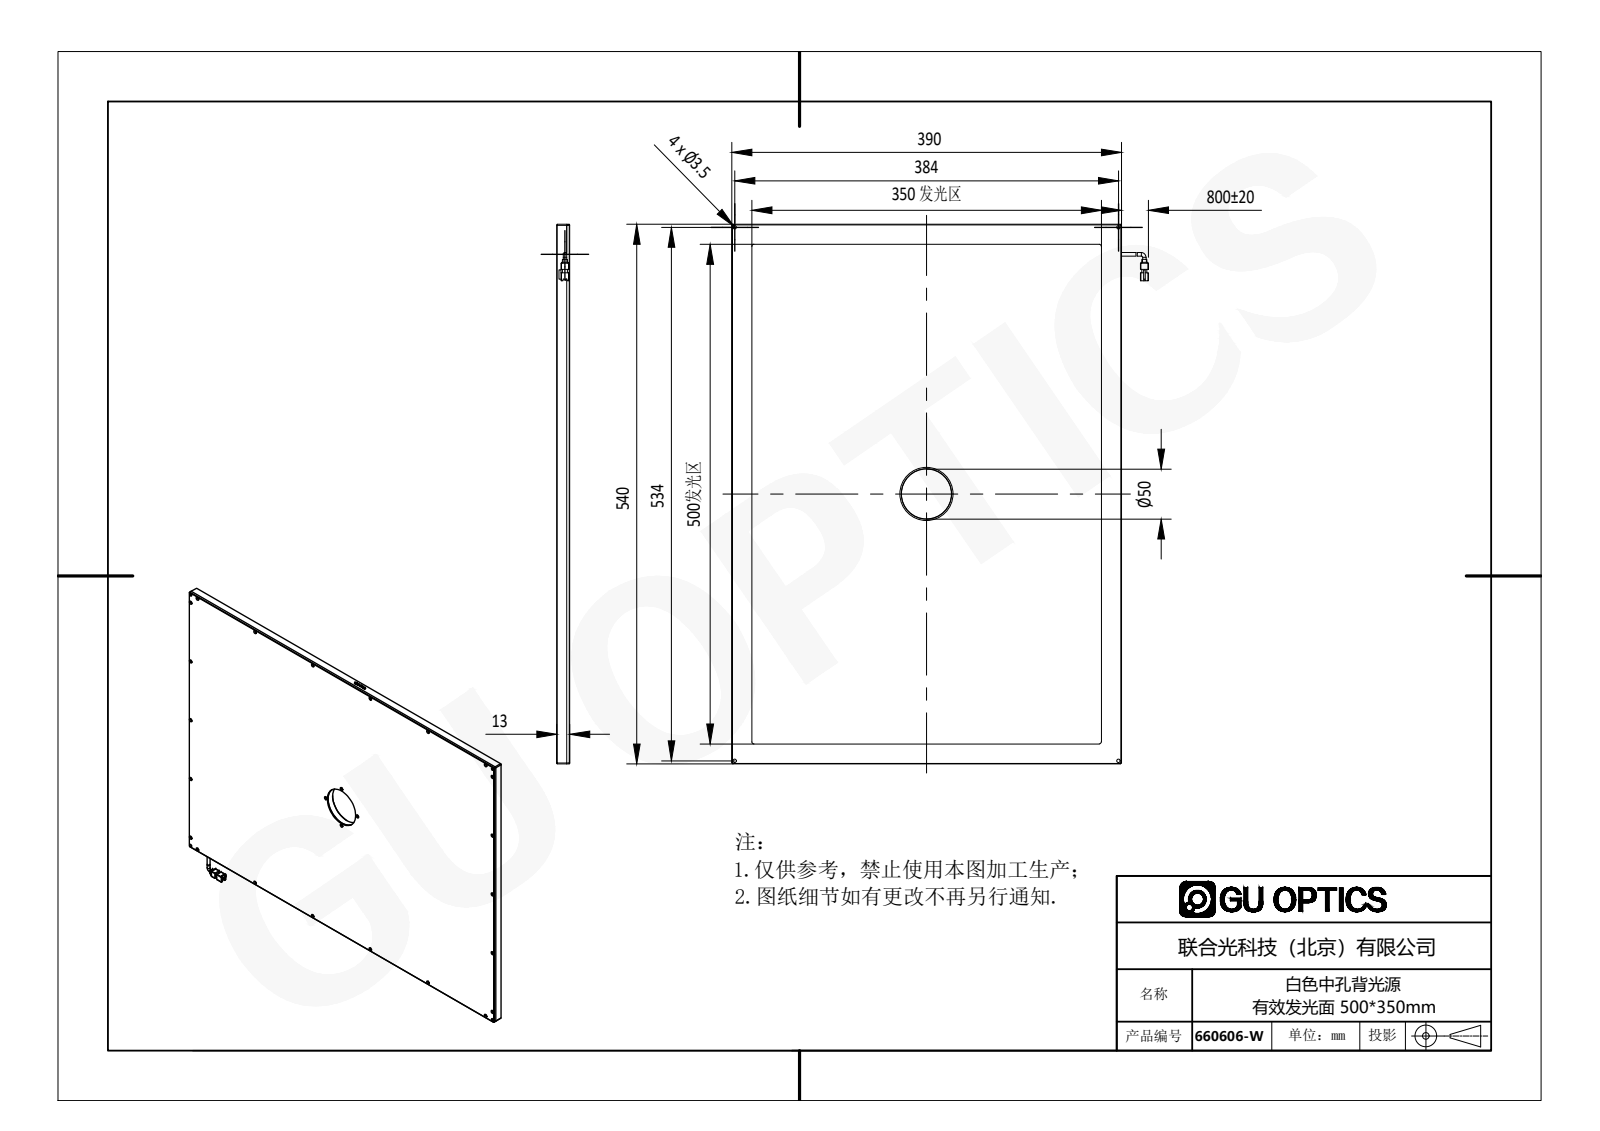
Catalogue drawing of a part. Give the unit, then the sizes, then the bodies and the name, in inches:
Units: inches
Overall size (bounding box): 21.26 × 16.417 × 0.512
Round holes (diameter × count): ⌀0.079 ×26, ⌀0.063 ×22, ⌀0.094 ×22, ⌀0.138 ×4, ⌀1.969 ×1, ⌀2.087 ×1, ⌀2.37 ×1
Round bosses / shafts (diameter × count): ⌀0.138 ×2, ⌀2.362 ×1
Partial cylindrical surfaces — rounded edges, fillets, slot ends (radius × count): R0.02 ×8, R0.039 ×6, R0.059 ×4, R0.079 ×4
Main face-to-face distances: 0.256, 0.118, 0.374, 0.512, 0.138, 0.394, 0.079, 0.236, 0.315, 15.118
Hole centre spacings: 4.016, 15.643, 0.472, 3.543, 8.031, 15.118, 17.119, 21.32
Volume: 127.2 in³ · Surface area: 1 462 in²
Bodies: 7 solids, 987 faces (622 planar, 204 cylindrical, 161 other)
Part name (STEP PRODUCT): 660606-W
STEP written by: SolidWorks 2016 (AUTOMOTIVE_DESIGN)
